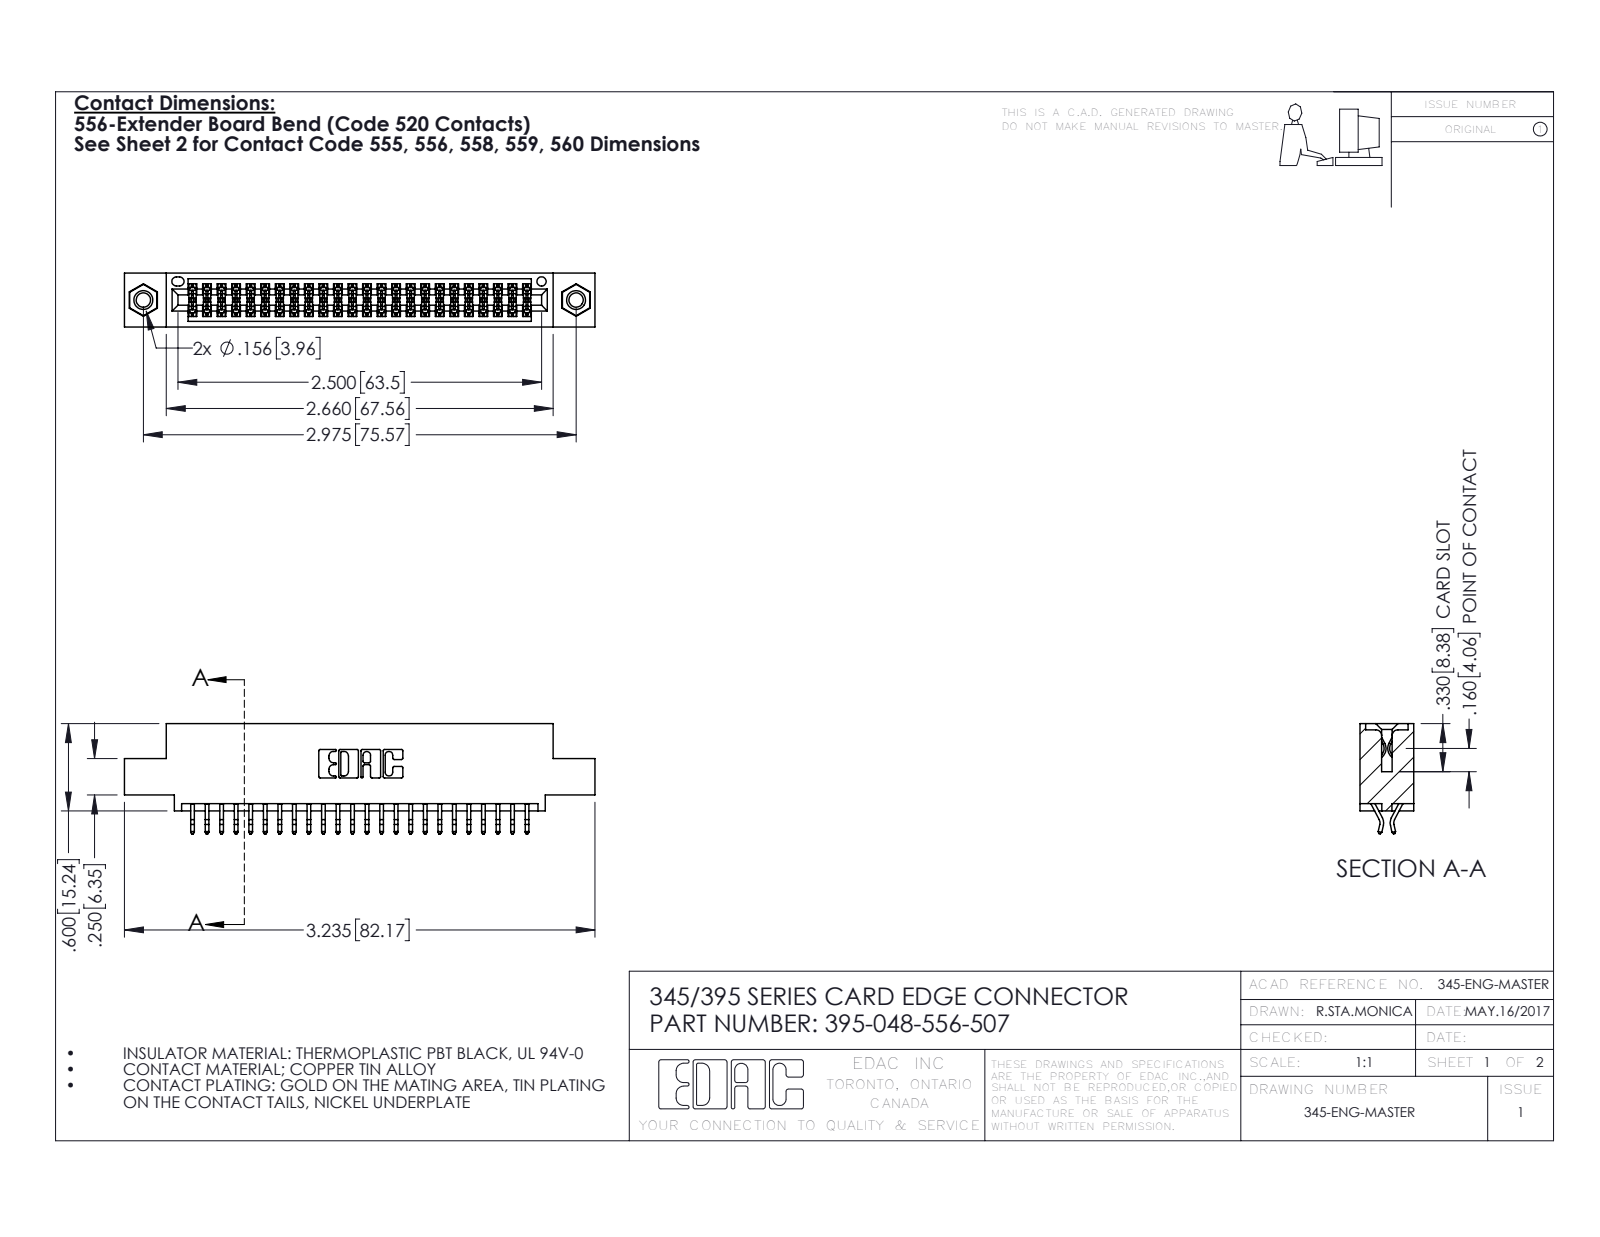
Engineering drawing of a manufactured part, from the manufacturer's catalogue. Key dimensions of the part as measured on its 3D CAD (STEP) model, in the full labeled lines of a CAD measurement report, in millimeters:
Part name (STEP PRODUCT): 395-048-556-507; 345-250-001_345-250-005-103; 345-292-001_556 Tail; 345 Part_0.110 Offset - 0.156 Dia-TI
STEP written by: SolidWorks 2016 (CONFIG_CONTROL_DESIGN)
Units: millimetres
Bodies: 51 solids, 2878 faces (1892 planar, 970 cylindrical, 16 other)
Overall size (bounding box): 82.2 × 19.2 × 9.4
Volume: 7 720 mm³ · Surface area: 11 150 mm²
Round holes (diameter × count): ⌀2.5 ×2, ⌀3.2 ×2, ⌀4 ×2, ⌀1.6 ×1
Round bosses / shafts (diameter × count): ⌀3.9 ×2
Partial cylindrical surfaces — rounded edges, fillets, slot ends (radius × count): R0.2 ×72, R0.3 ×22, R0.2 ×6, R0.8 ×6, R0.7 ×3, R0.3 ×2, R0.4 ×2, R0.5 ×2
Main face-to-face distances: 1.8, 7.6, 5.1, 9.4, 0.6, 2.5, 6.9, 5.7, 4.4, 3.8
Hole centre spacings: 6.9, 69.6, 75.6
